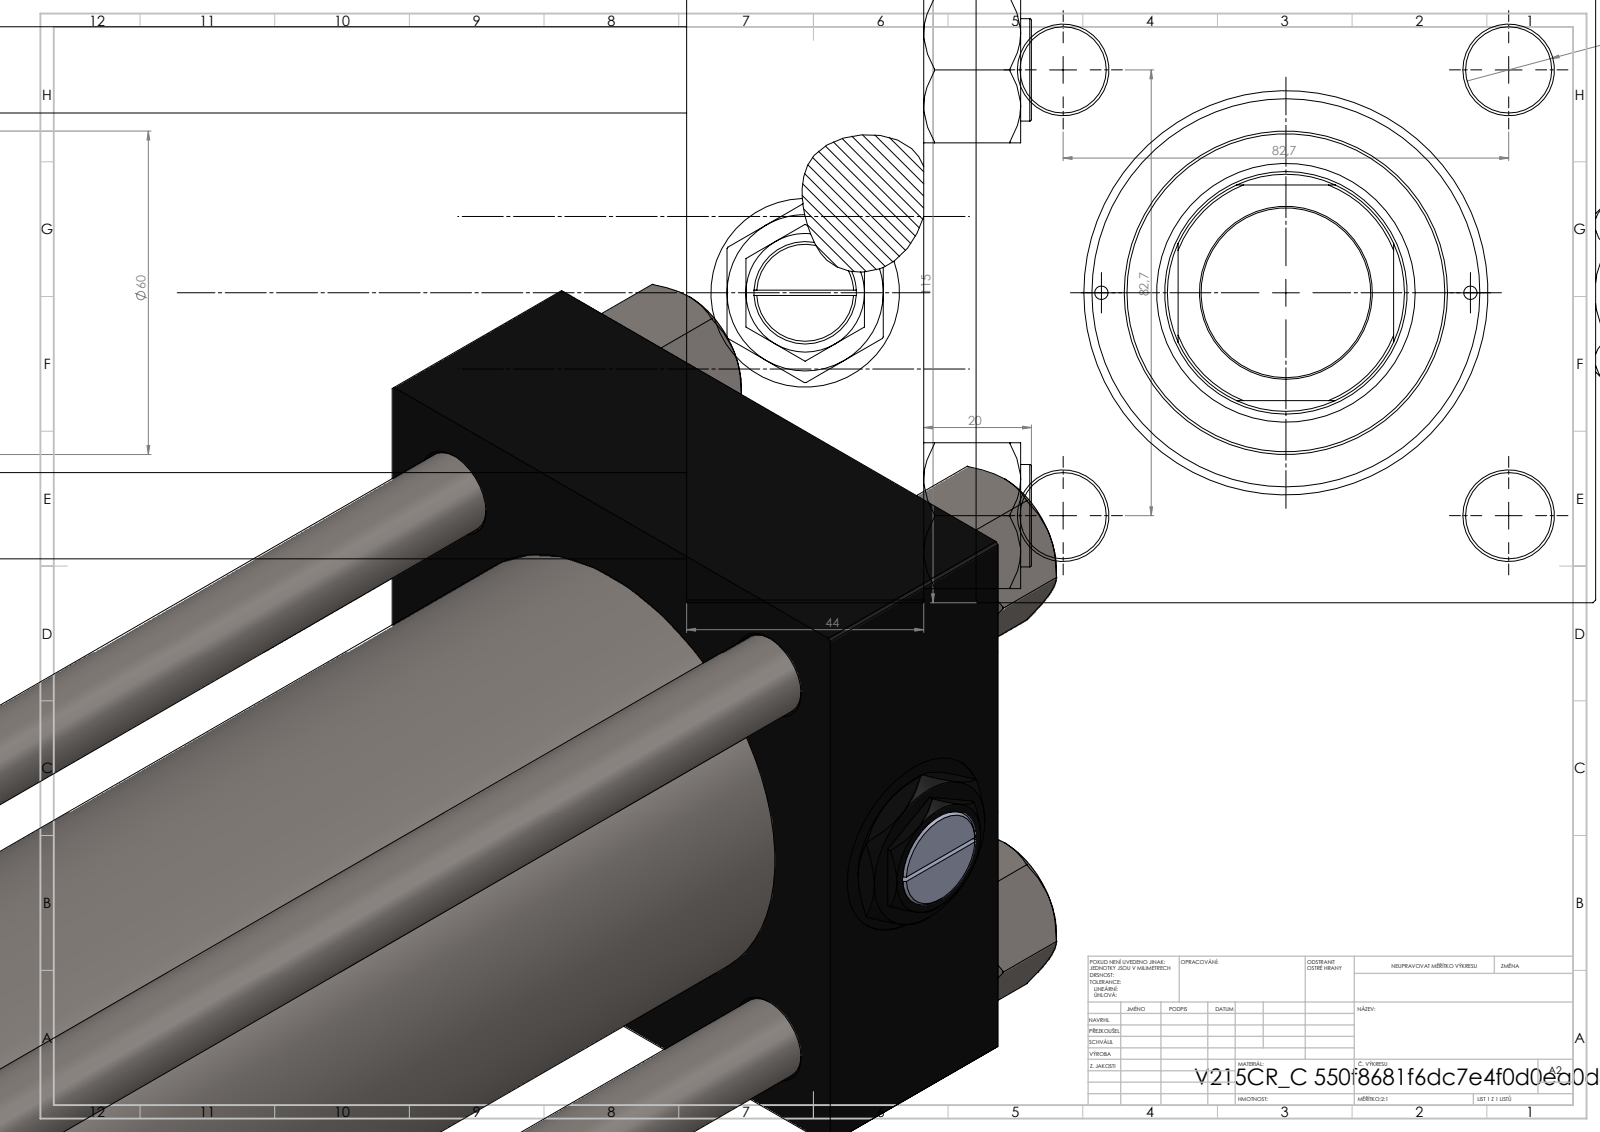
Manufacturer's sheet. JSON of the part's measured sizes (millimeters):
{"part_name": "V215CR_C_Body; NUT_M5_C; V215CR_C_TYCINKA; V215CR_VCP_C (+2 more)", "step_written_by": "SolidWorks 2019 (CONFIG_CONTROL_DESIGN)", "units": "millimeters", "bodies": {"solids": 13, "faces": 1303, "planar": 623, "cylindrical": 102, "other": 578}, "overall_size": [410, 122, 115], "volume_mm3": 2377000, "surface_area_mm2": 436380, "round_holes": [[16, 4], [2.5, 2], [7, 2], [26.44, 2], [35, 2], [31.5, 1], [45, 1], [48, 1], [61, 1], [72, 1], [80, 1]], "round_bosses_or_shafts": [[19, 4], [86, 1], [60, 1]], "partial_cylinders_radius": [[22, 1]], "face_to_face_distances": [115, 44, 359, 315, 69, 290, 246, 330.3, 286.3, 40.3], "hole_center_spacings": [41.96, 58.48, 82.7, 86.17, 34.25, 116.96, 68.5, 291]}
